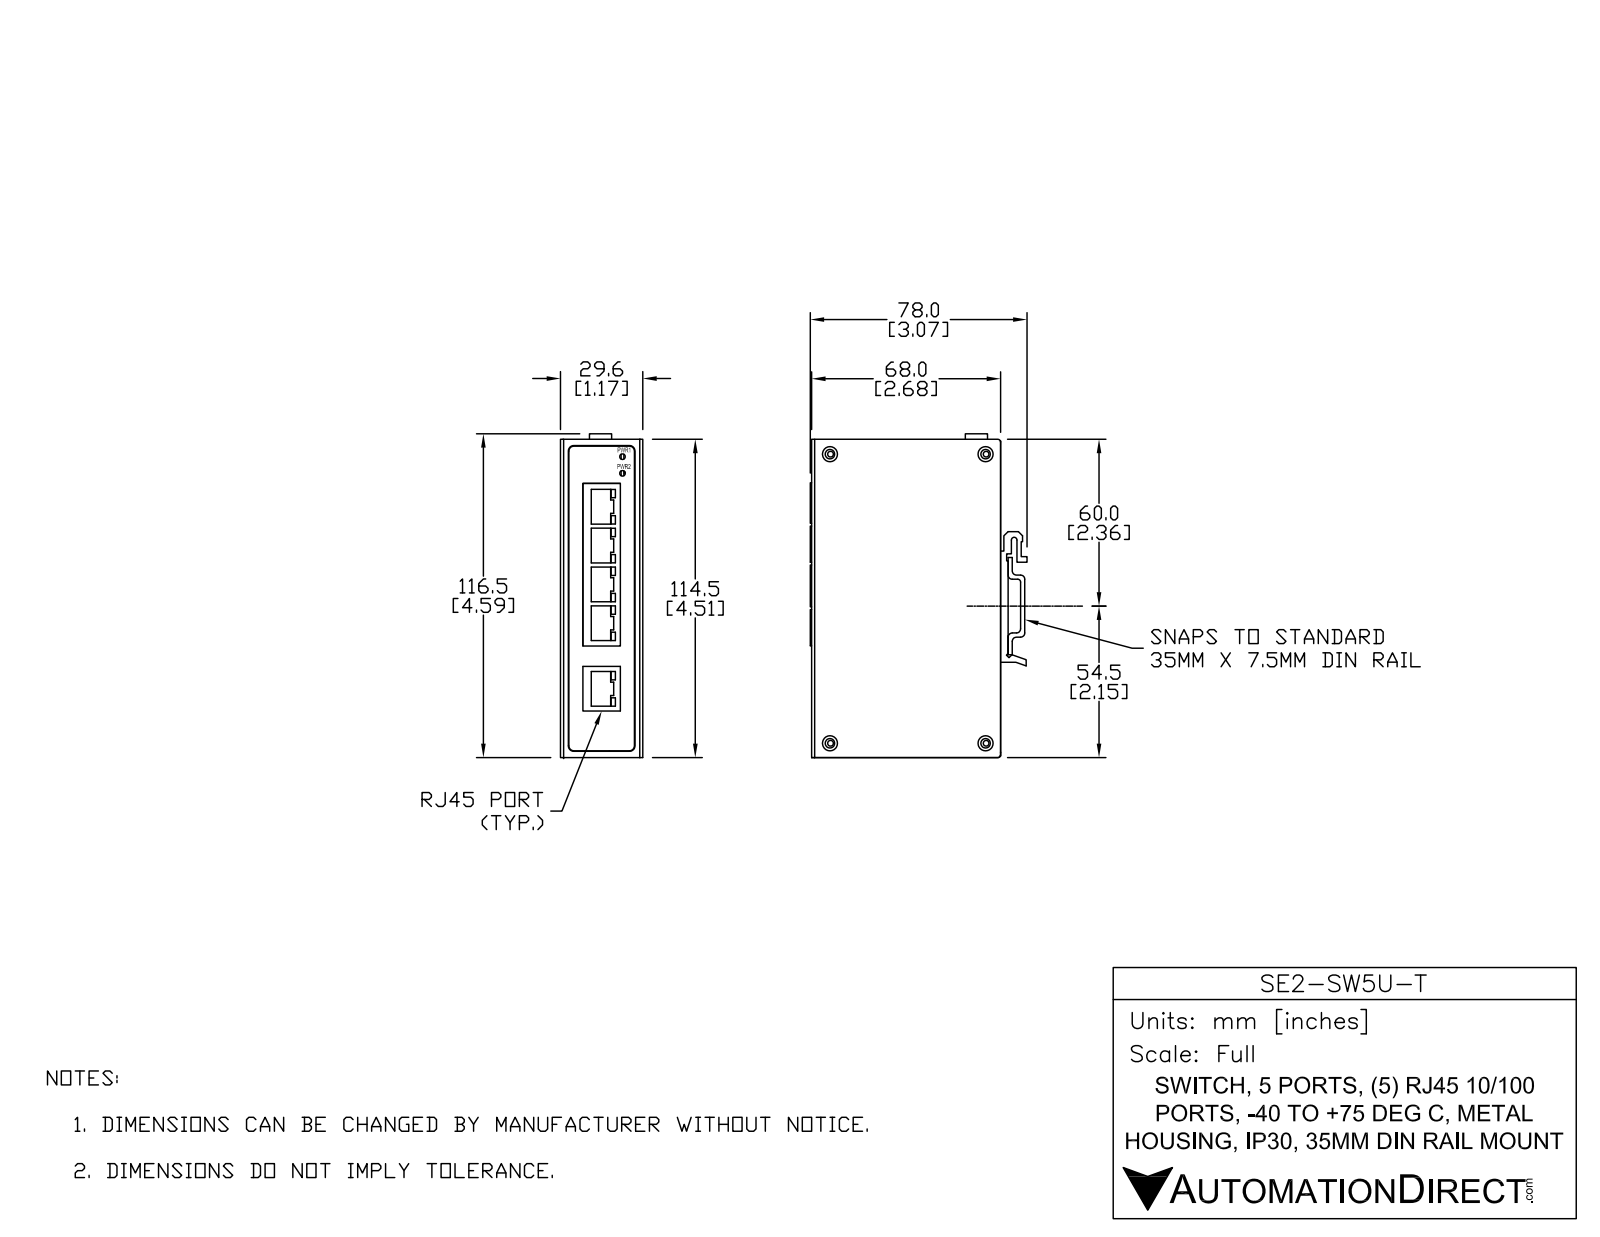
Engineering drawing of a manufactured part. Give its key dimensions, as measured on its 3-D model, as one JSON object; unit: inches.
{"part_name": "SE2-SW5U-T", "step_written_by": "SolidWorks 2017 (AUTOMOTIVE_DESIGN)", "units": "inches", "bodies": {"solids": 10, "faces": 938, "planar": 648, "cylindrical": 245, "other": 45}, "overall_size": [4.951, 3.047, 1.165], "volume_in3": 3.531, "surface_area_in2": 134.7, "round_holes": [[0.051, 4], [0.11, 4], [0.15, 4], [0.122, 3], [0.118, 2], [0.138, 2], [0.155, 1]], "round_bosses_or_shafts": [[0.142, 4], [0.118, 4], [0.051, 4], [0.024, 4], [0.197, 2], [0.315, 1], [0.157, 1]], "partial_cylinders_radius": [[0.024, 96], [0.026, 16], [0.079, 8], [0.118, 8], [0.041, 6], [0.039, 5], [0.012, 4], [0.112, 4]], "face_to_face_distances": [0.039, 0.02, 1.087, 1.126, 0.079, 1.047, 1.067, 1.106, 0.059, 1.028], "hole_center_spacings": [0.2, 2.205, 0.203, 0.4, 0.4, 0.543, 0.543, 0.574]}
